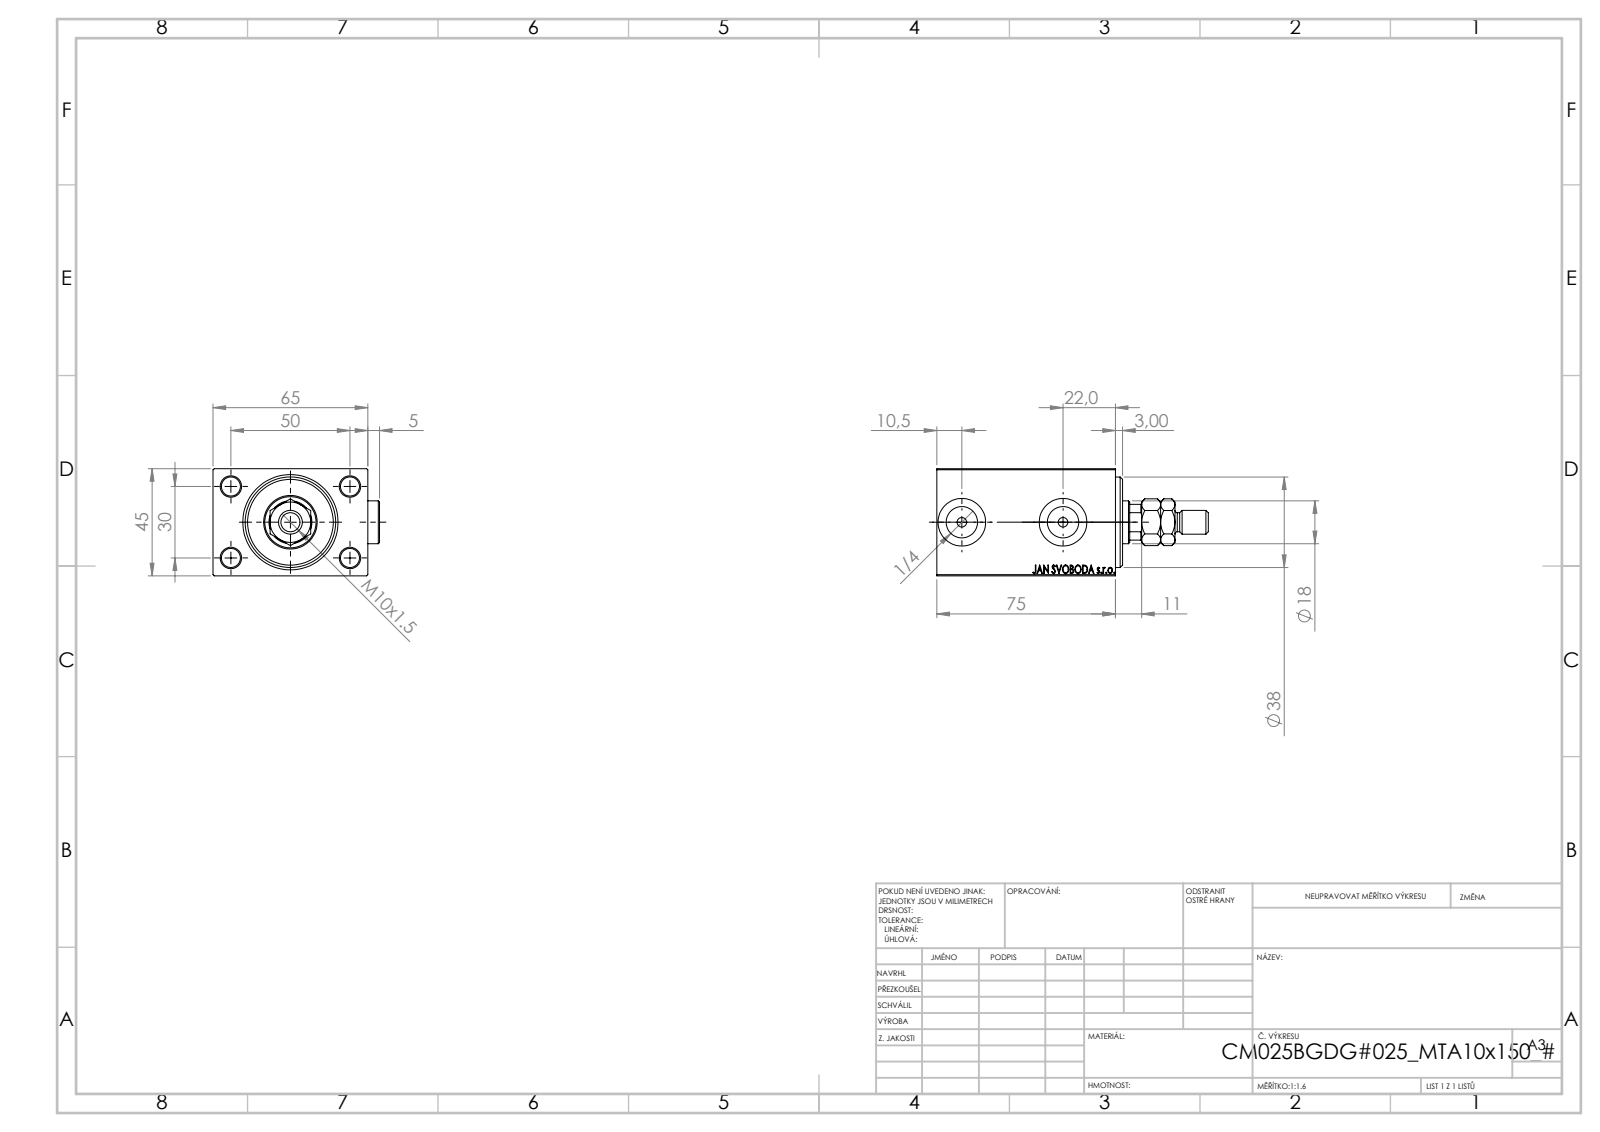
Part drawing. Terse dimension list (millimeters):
name: MTA; V450CM_VC_B; V450CM_B_Body; V450CM_B_VCP (+1 more)
written by: SolidWorks 2019 (CONFIG_CONTROL_DESIGN)
unit: mm
bodies: 6 solids, 984 faces (450 planar, 74 cylindrical, 460 other)
size: 114 × 69.9 × 45
volume: 210 272 mm³; area: 47 416 mm²
holes: 4× ⌀8, 2× ⌀4, 2× ⌀13.16, 2× ⌀20, 1× ⌀8.5, 1× ⌀18, 1× ⌀21.5, 1× ⌀22.5, 1× ⌀25, 1× ⌀27, 1× ⌀38
bosses: 2× ⌀18, 1× ⌀10, 1× ⌀8
rounds: 1× R8.5
face distances: 45, 65, 5, 75, 6, 64, 64.9, 70, 69, 8
hole spacings: 29.15, 30, 50, 58.31, 42.5
